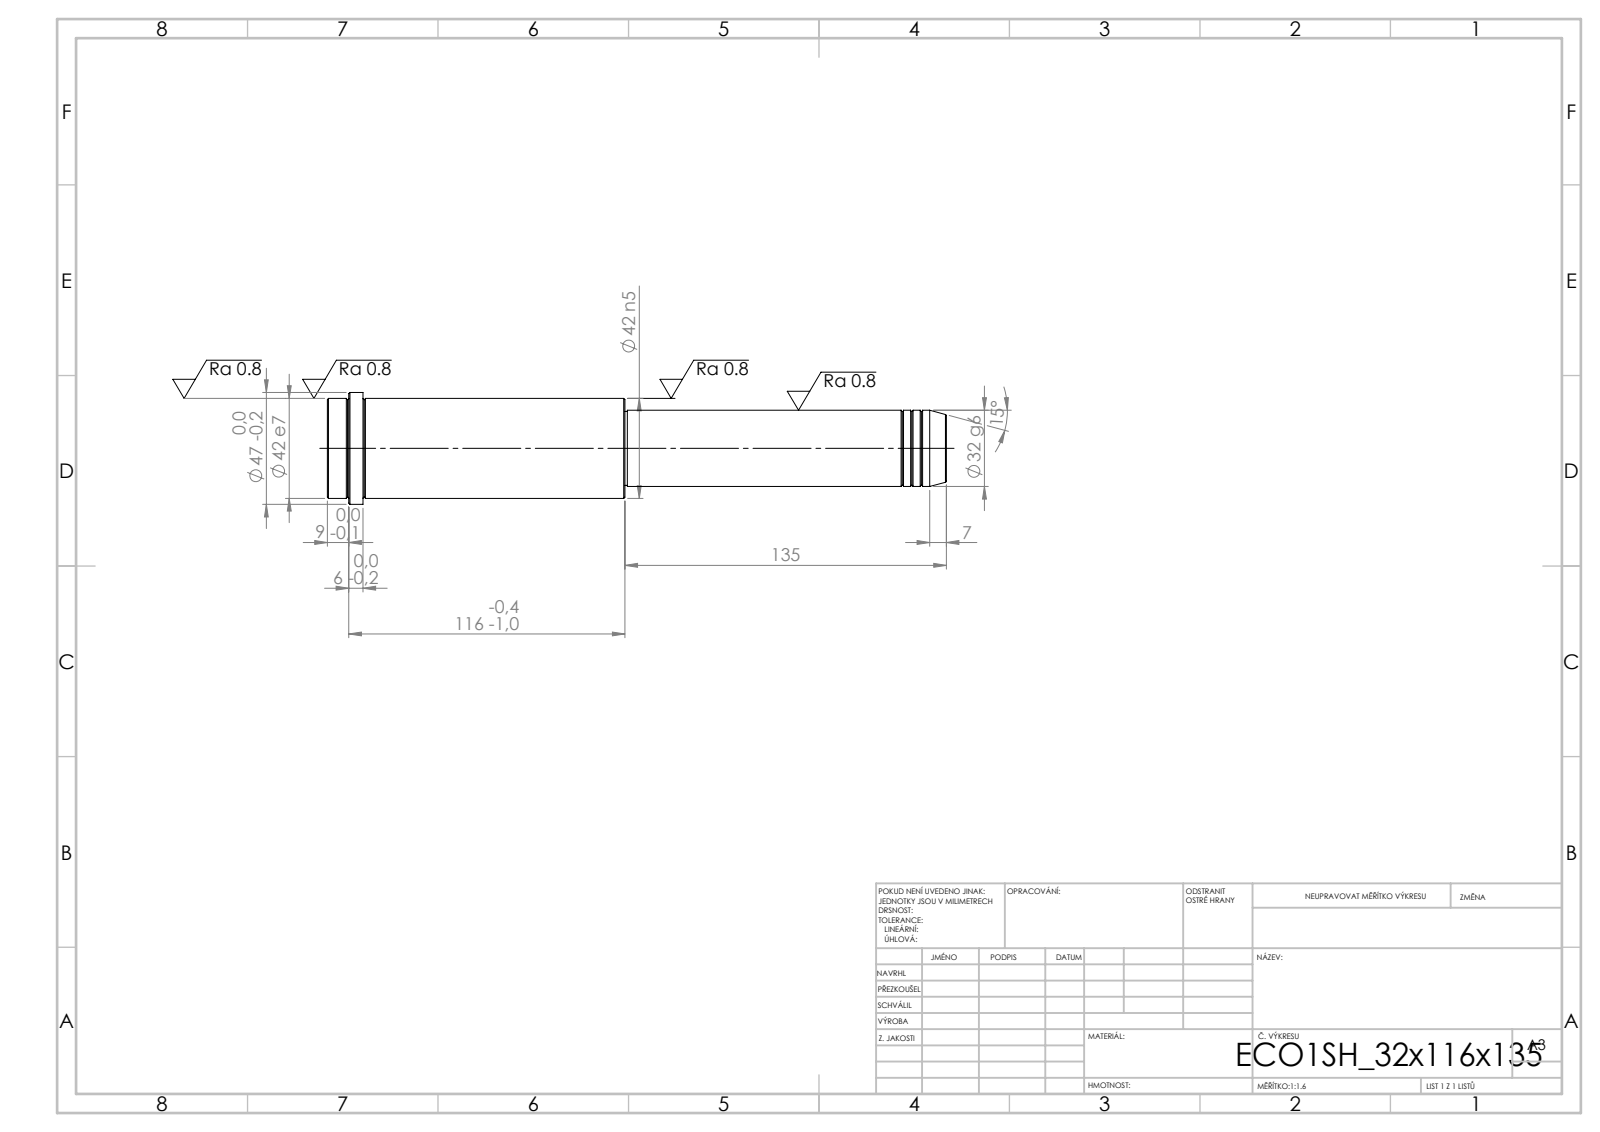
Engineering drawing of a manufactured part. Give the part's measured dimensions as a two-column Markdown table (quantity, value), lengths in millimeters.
| quantity | value |
| --- | --- |
| STEP written by | SolidWorks 2019 (CONFIG_CONTROL_DESIGN) |
| units | millimeters |
| bodies | 1 solid, 52 faces (6 planar, 16 cylindrical, 30 other) |
| overall size | 260 × 47 × 47 |
| volume | 282 894 mm³ |
| surface area | 33 705 mm² |
| round bosses / shafts (diameter × count) | 47 × 1, 42 × 1, 32 × 1, 31 × 1 |
| main face-to-face distances | 260, 135, 125, 245, 110, 15, 251, 116, 6, 9 |
